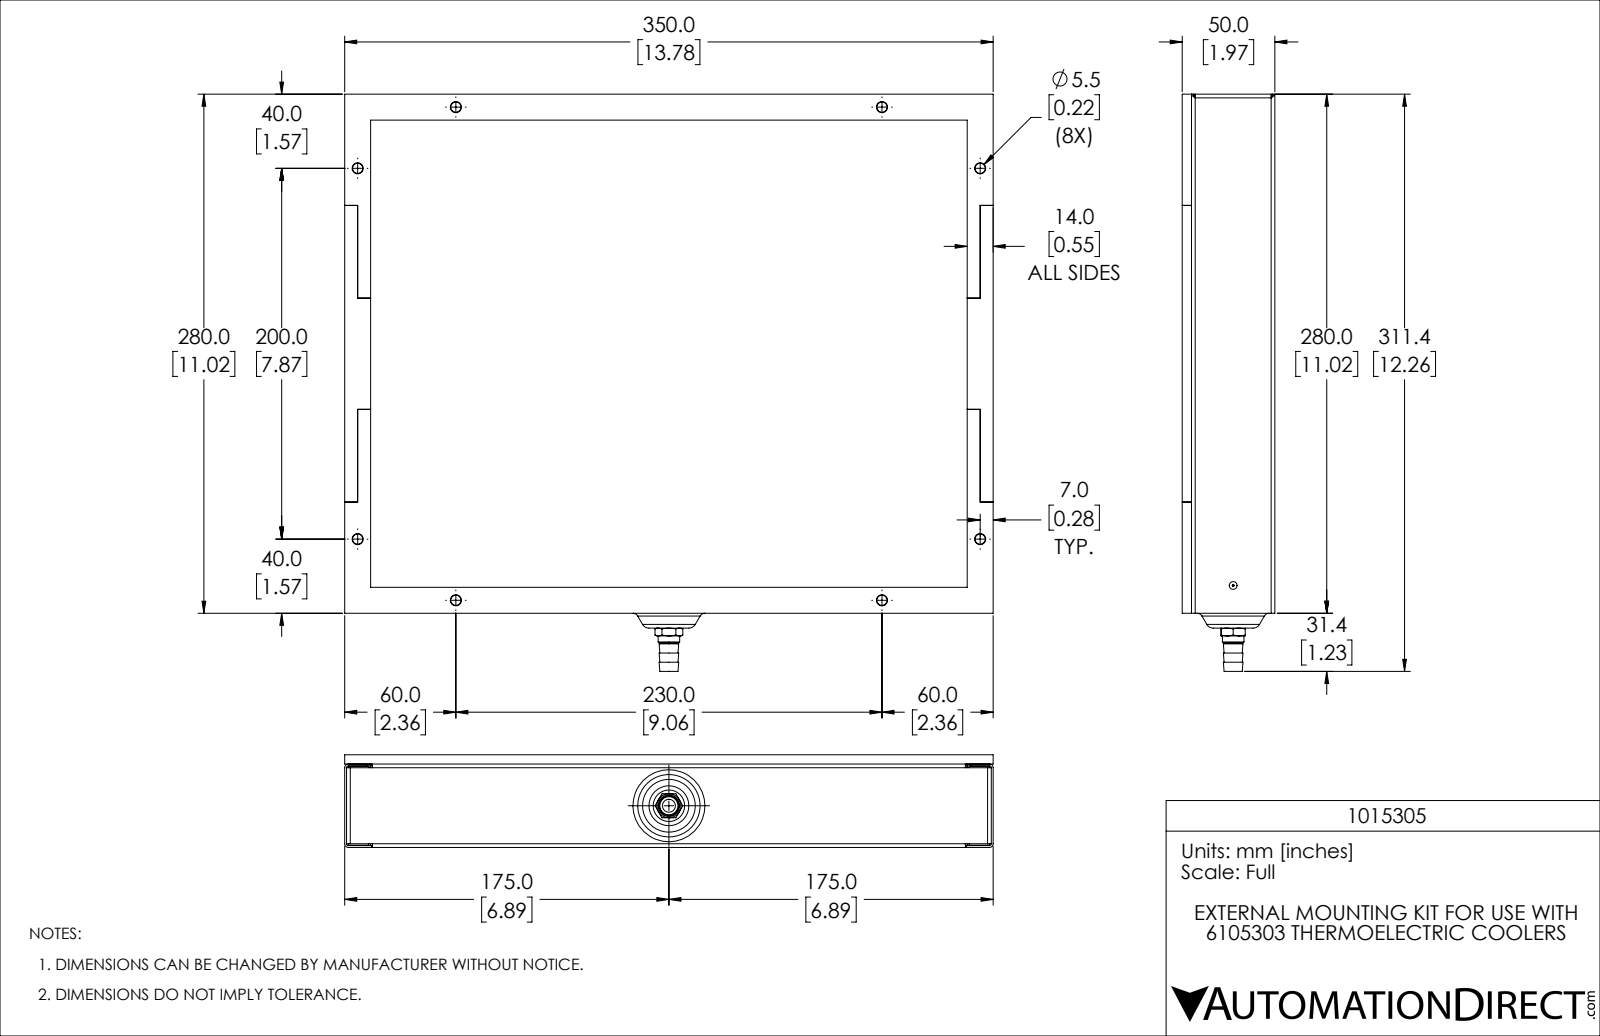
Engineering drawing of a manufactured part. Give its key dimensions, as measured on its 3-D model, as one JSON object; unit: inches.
{"part_name": "1015305", "step_written_by": "SolidWorks 2019 (AUTOMOTIVE_DESIGN)", "units": "inches", "bodies": {"solids": 9, "faces": 371, "planar": 258, "cylindrical": 70, "other": 43}, "overall_size": [13.78, 12.258, 1.969], "volume_in3": 11.43, "surface_area_in2": 401.7, "round_holes": [[0.217, 8], [0.236, 8], [0.177, 1], [0.276, 1], [0.433, 1], [0.484, 1], [0.492, 1]], "round_bosses_or_shafts": [[0.746, 1], [0.669, 1], [0.457, 1], [0.387, 1]], "partial_cylinders_radius": [[0.039, 20], [0.079, 20], [0.157, 2]], "face_to_face_distances": [0.039, 0.512, 10.984, 13.74, 1.732, 0.551, 10.472, 0.197, 0.236, 13.228], "hole_center_spacings": [2.458, 9.407, 11.217, 14.432, 7.874, 9.055, 10.472, 13.228]}
